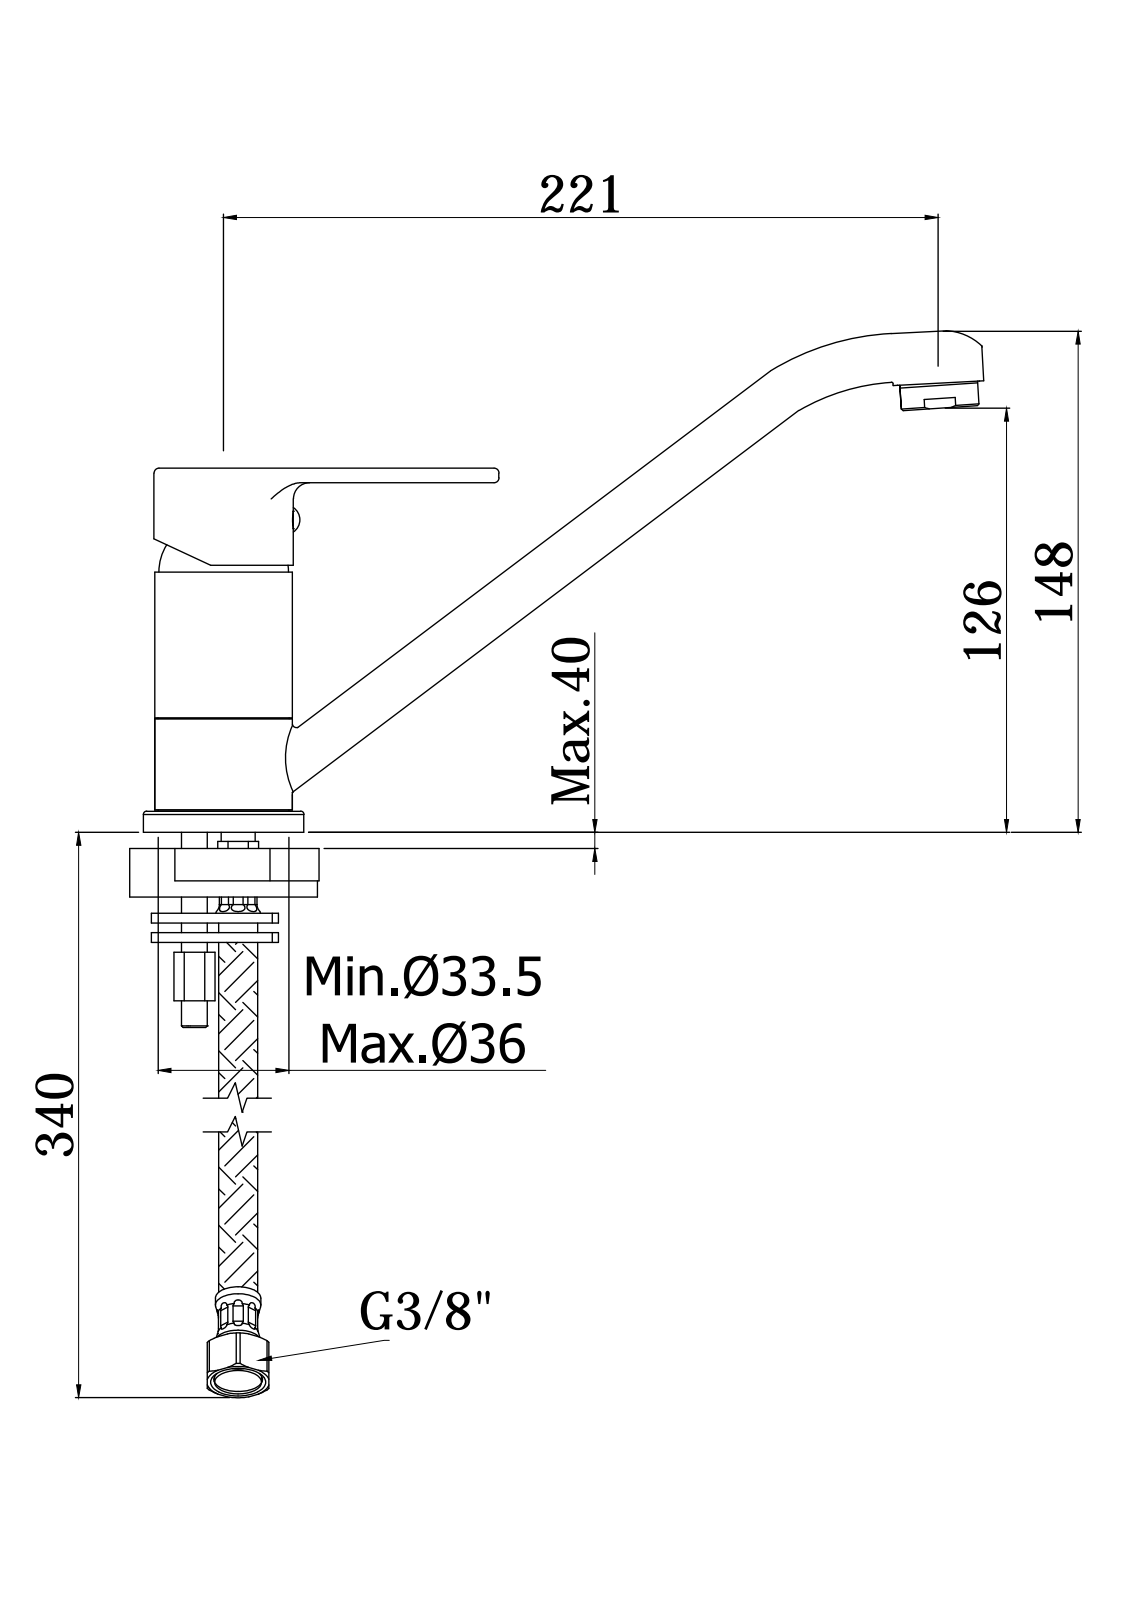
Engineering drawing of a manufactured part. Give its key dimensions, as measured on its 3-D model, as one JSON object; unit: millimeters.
{"part_name": "RED182TCR", "step_written_by": "CREO PARAMETRIC BY PTC INC, 2020044 (CONFIG_CONTROL_DESIGN)", "units": "millimeters", "bodies": {"solids": 3, "faces": 2625, "planar": 2039, "cylindrical": 339, "other": 247}, "overall_size": [258.72, 156.82, 49.5], "volume_mm3": 132926, "surface_area_mm2": 100445, "round_holes": [[9, 4], [8, 3], [3.3, 2], [4, 2], [11, 2], [3, 1], [4.5, 1], [5, 1], [6.8, 1], [16, 1], [17, 1], [19.5, 1]], "round_bosses_or_shafts": [[49.5, 1], [43, 1], [42.5, 1], [40.4, 1], [36.6, 1], [35, 1], [34.8, 1], [34, 1]], "partial_cylinders_radius": [[0.5, 66], [0.15, 11], [0.3, 4], [1.5, 4], [4.25, 4], [5.5, 4], [1, 2], [5, 2]], "face_to_face_distances": [1.25, 4.5, 1, 5.8, 5.5, 107.5, 58.3, 62.8, 106.5, 9.5], "hole_center_spacings": [0.5, 8.32, 8.6, 11.6, 12, 14, 14.01, 15.21]}
